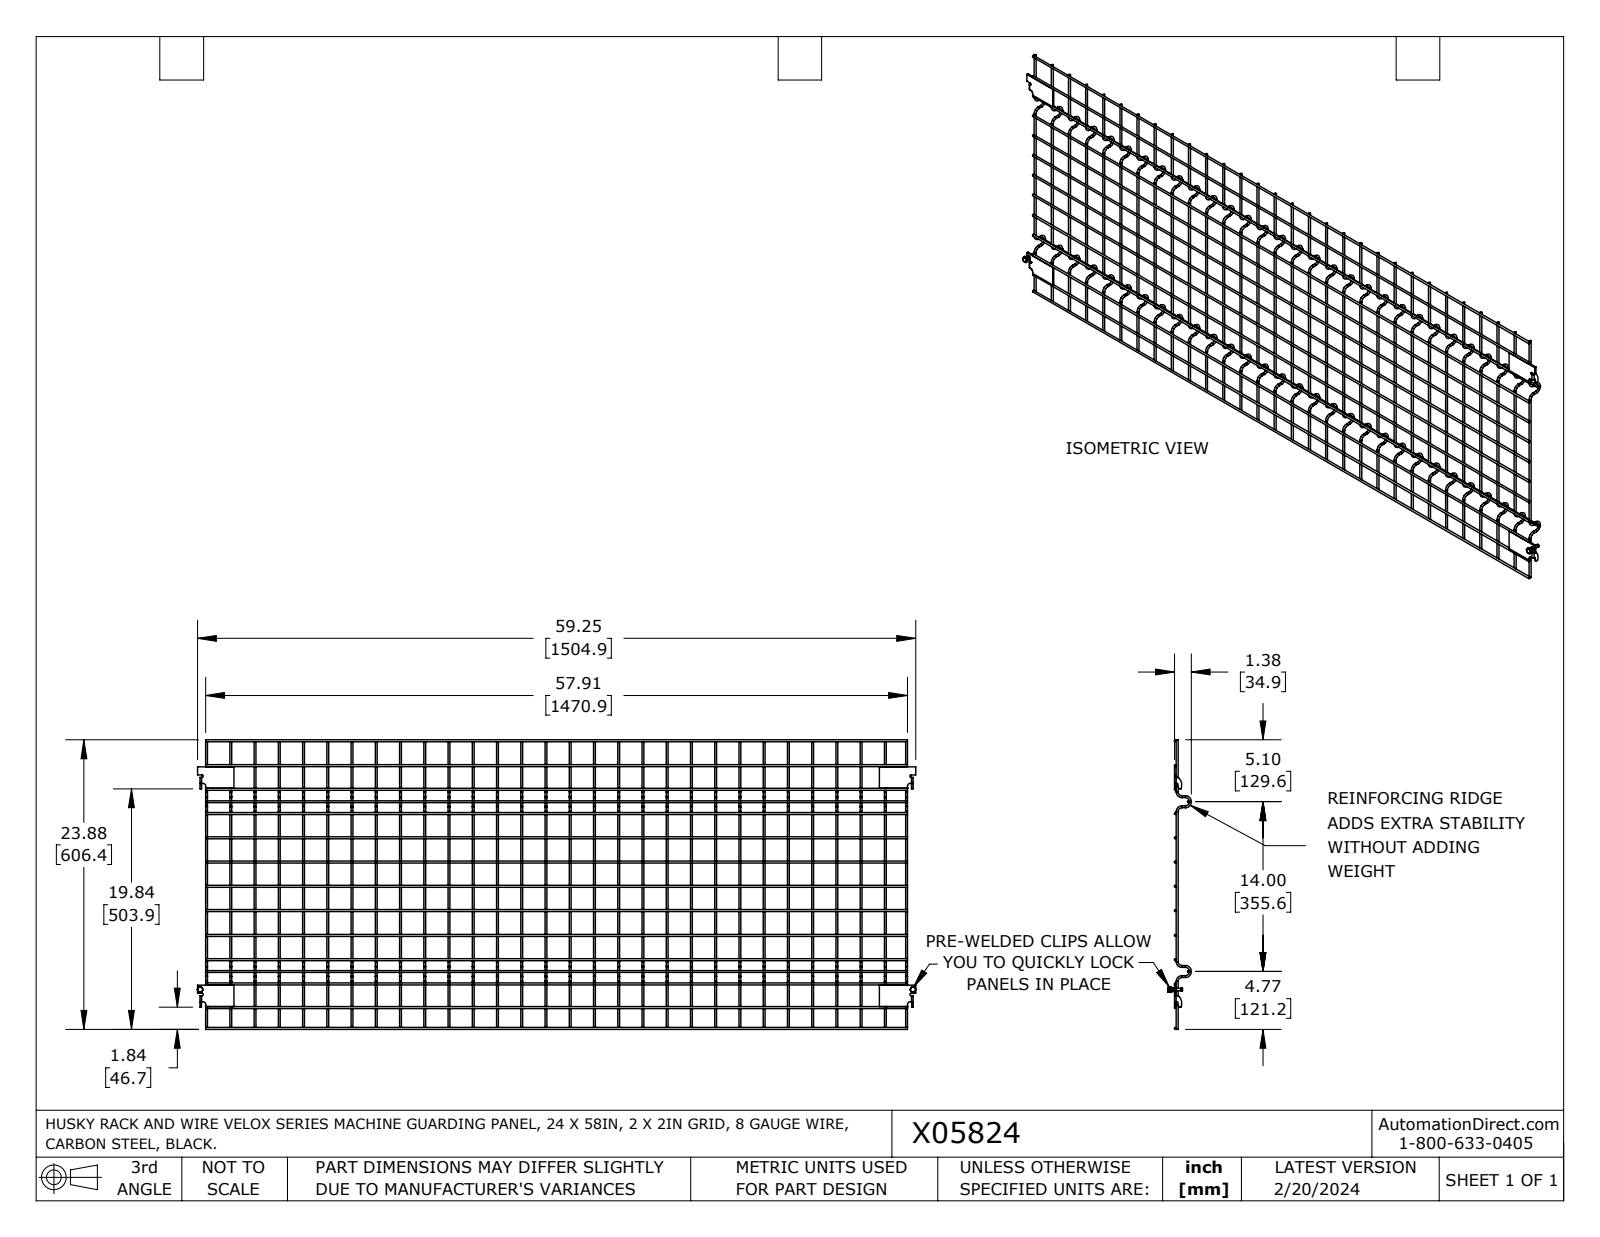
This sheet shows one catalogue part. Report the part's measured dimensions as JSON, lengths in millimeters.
{"part_name": "X05824", "step_written_by": "SolidWorks 2023 (AUTOMOTIVE_DESIGN)", "units": "millimeters", "bodies": {"solids": 53, "faces": 755, "planar": 170, "cylindrical": 321, "other": 264}, "overall_size": [1506.6, 606.4, 47.1], "volume_mm3": 597000, "surface_area_mm2": 576500, "round_holes": [[5.1, 2], [6.4, 2]], "round_bosses_or_shafts": [[4.1, 195], [9.9, 2], [6.2, 2], [4.7, 2]], "partial_cylinders_radius": [[2.5, 4], [5.5, 4], [0.2, 2], [1.7, 2], [3.4, 2], [6.4, 2], [22, 2]], "face_to_face_distances": [3.4, 3.2, 71.1, 1423.6, 457.2, 457.2, 11.9, 1482.8, 59.2, 1411.7], "hole_center_spacings": [1493.7]}
